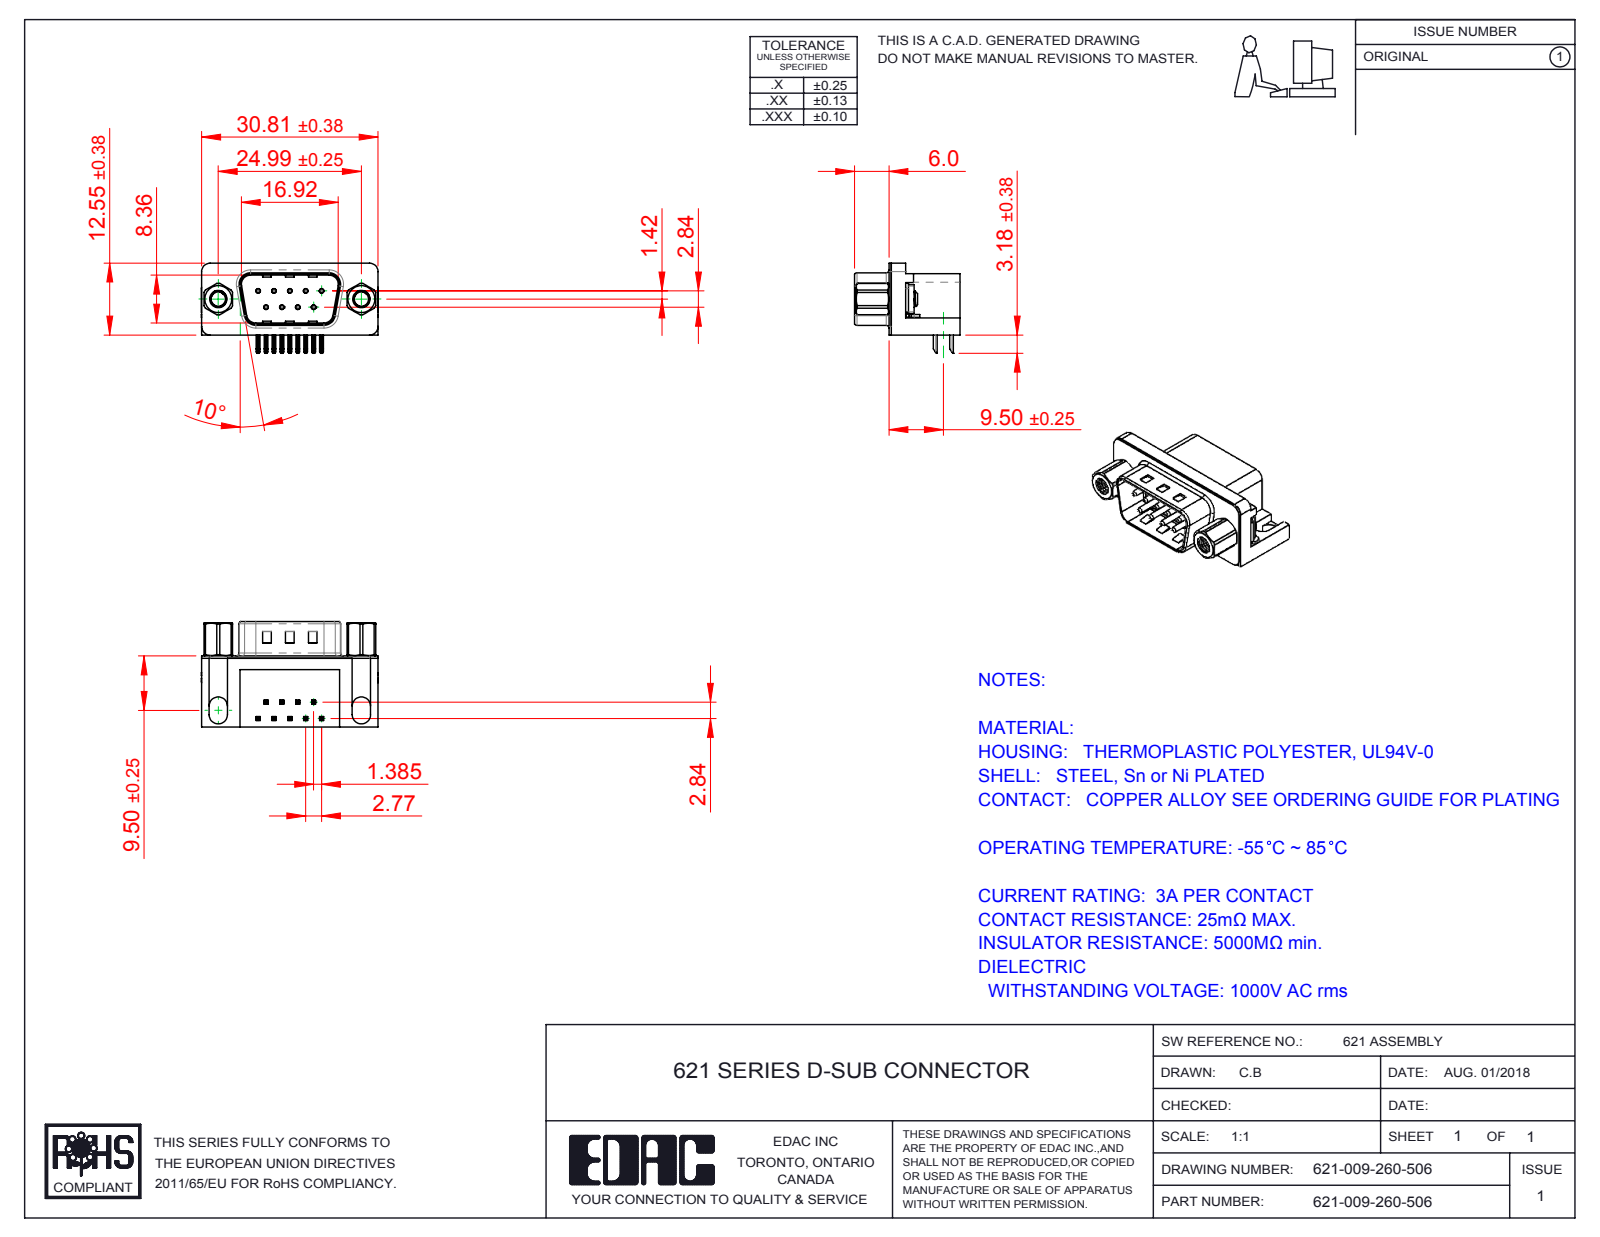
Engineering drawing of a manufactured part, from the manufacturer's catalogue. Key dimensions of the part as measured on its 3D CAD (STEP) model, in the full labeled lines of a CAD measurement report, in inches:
Part name (STEP PRODUCT): 621 Contact Bottom; 621 Housing_9 Socket; 621 Non Board Mount; 621 M3 Threaded Rivet (+4 more)
STEP written by: SolidWorks 2016 (CONFIG_CONTROL_DESIGN)
Units: inches
Bodies: 17 solids, 1133 faces (593 planar, 407 cylindrical, 133 other)
Overall size (bounding box): 1.216 × 0.724 × 0.619
Volume: 0.21 in³ · Surface area: 7.409 in²
Round holes (diameter × count): ⌀0.014 ×9, ⌀0.031 ×9, ⌀0.098 ×2, ⌀0.157 ×2, ⌀0.189 ×2, ⌀0.197 ×2
Round bosses / shafts (diameter × count): ⌀0.03 ×9, ⌀0.193 ×2, ⌀0.187 ×2, ⌀0.154 ×2, ⌀0.118 ×2
Partial cylindrical surfaces — rounded edges, fillets, slot ends (radius × count): R0.01 ×44, R0.005 ×18, R0.039 ×16, R0.02 ×9, R0.059 ×8, R0.063 ×8, R0.035 ×4, R0.079 ×4
Main face-to-face distances: 0.016, 0.472, 0.488, 0.407, 0.374, 0.098, 0.114, 0.083, 0.014, 0.421
Hole centre spacings: 0.124, 0.109, 0.218, 0.198, 0.198, 0.327, 0.294, 0.295
